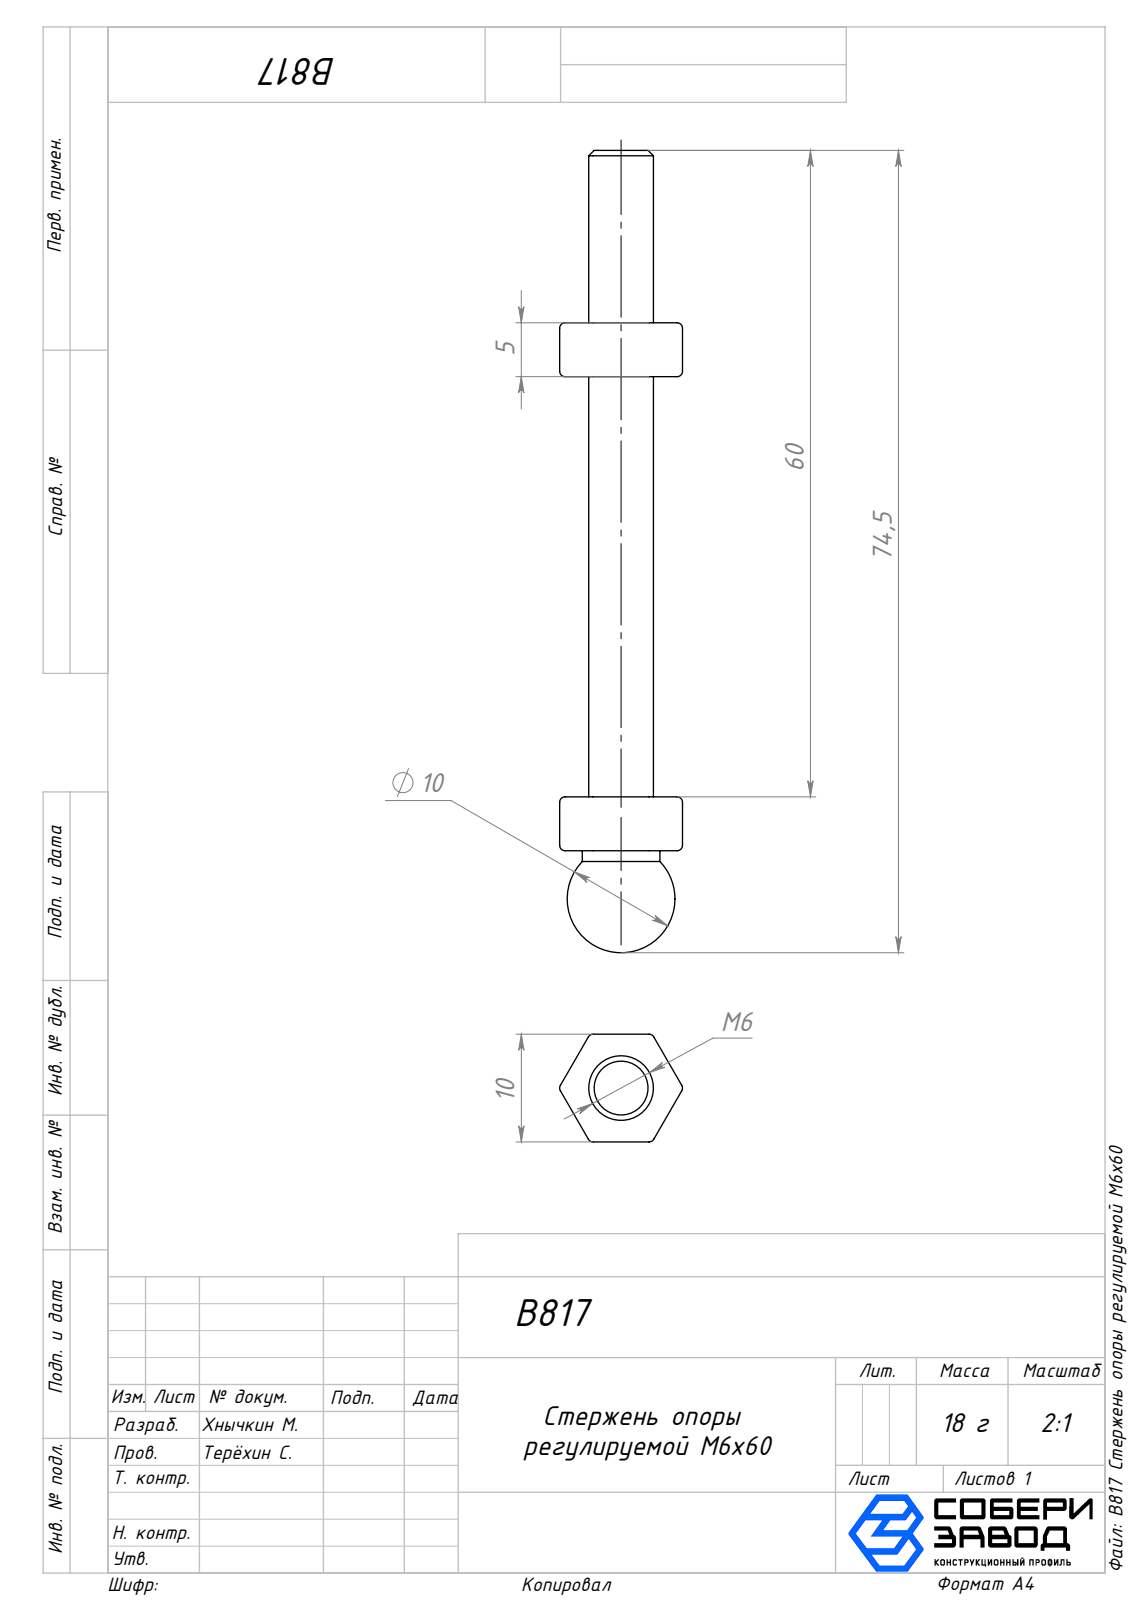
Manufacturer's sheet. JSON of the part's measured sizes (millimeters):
{"part_name": "Стержень_00; Гайка_00; B817 Стержень опоры регулируемой М6х60", "step_written_by": "SolidWorks 2025 (AUTOMOTIVE_DESIGN)", "units": "millimeters", "bodies": {"solids": 2, "faces": 92, "planar": 17, "cylindrical": 42, "other": 33}, "overall_size": [74.47, 11.39, 10], "volume_mm3": 2981, "surface_area_mm2": 2063, "round_holes": [[5, 1]], "round_bosses_or_shafts": [[7.2, 1], [6, 1]], "partial_cylinders_radius": [[0.5, 30]], "face_to_face_distances": [10, 5, 44, 39, 49, 65, 60, 21, 16]}
